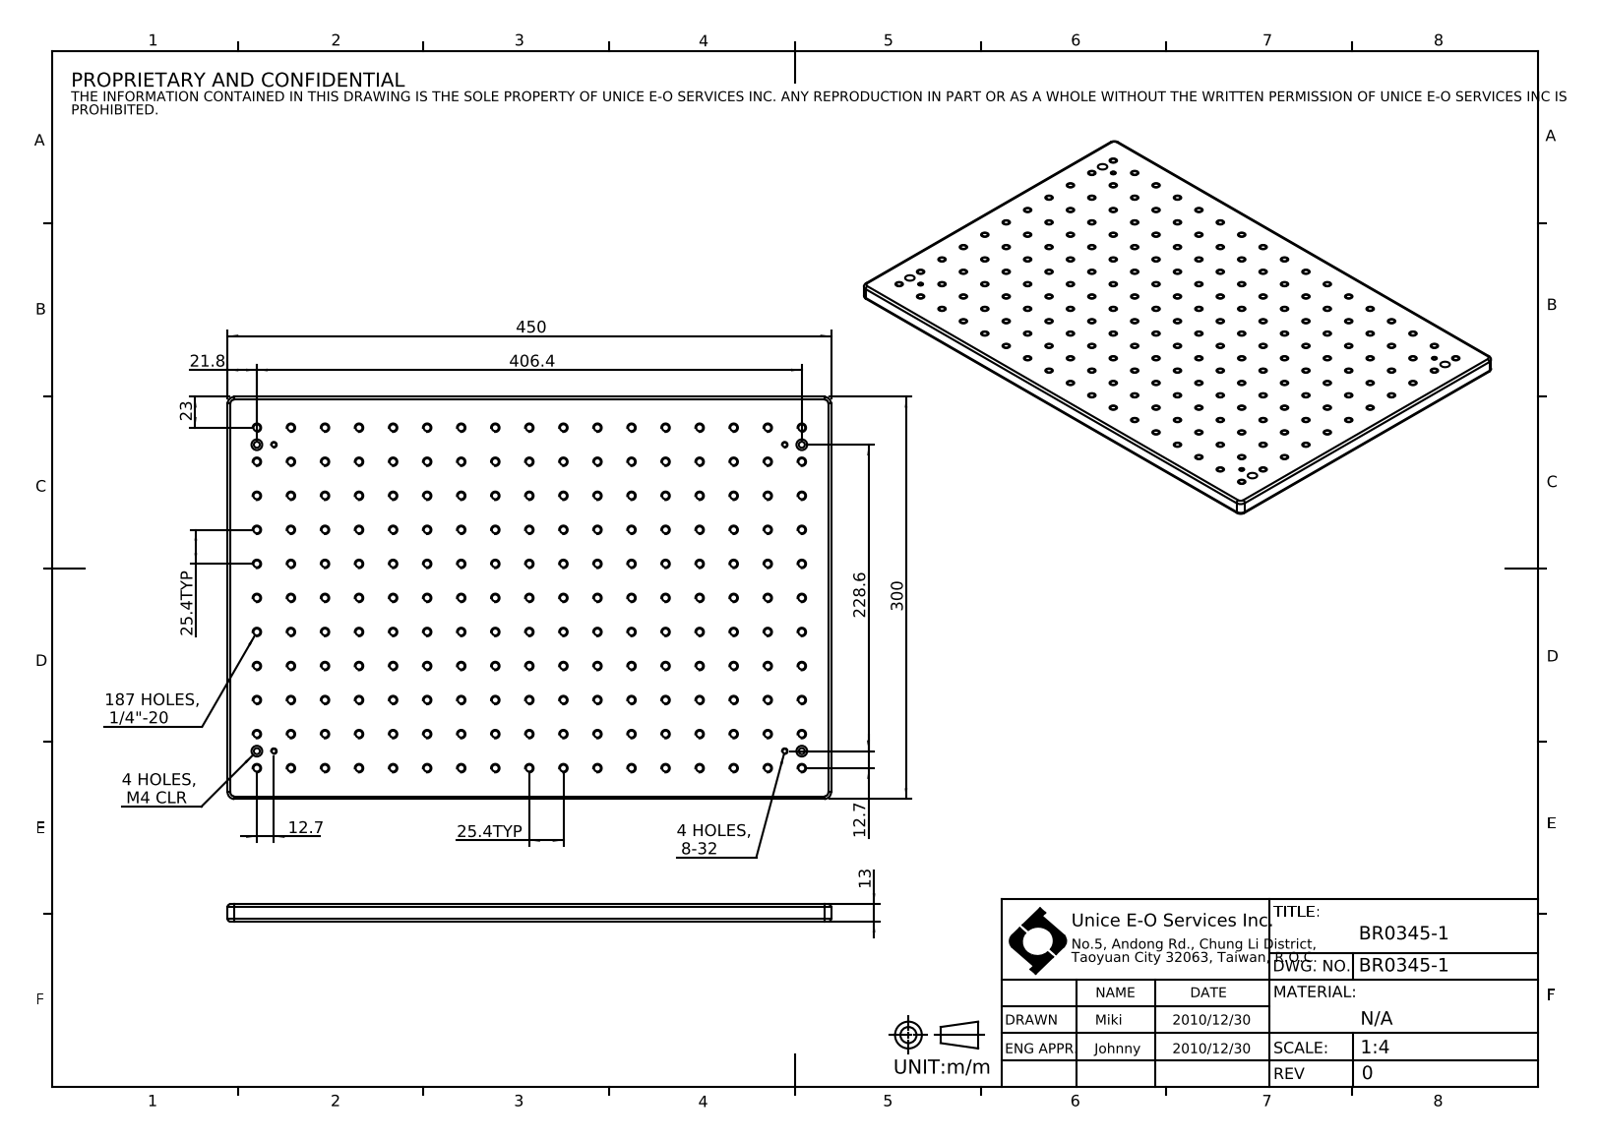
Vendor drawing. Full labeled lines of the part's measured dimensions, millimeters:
Part name (STEP PRODUCT): BR0345-1
STEP written by: SolidWorks 2016 (CONFIG_CONTROL_DESIGN)
Units: millimetres
Bodies: 1 solid, 428 faces (10 planar, 410 cylindrical, 8 other)
Overall size (bounding box): 450 × 300 × 13
Volume: 1 700 000 mm³ · Surface area: 319 477 mm²
Round holes (diameter × count): ⌀5.11 ×187, ⌀3.45 ×4, ⌀4.5 ×4, ⌀8 ×4
Partial cylindrical surfaces — rounded edges, fillets, slot ends (radius × count): R2 ×8, R5 ×4
Main face-to-face distances: 13, 300, 450, 7, 6
Hole centre spacings: 25.4, 50.8, 76.2, 101.6, 127, 228.6, 152.4, 177.8
